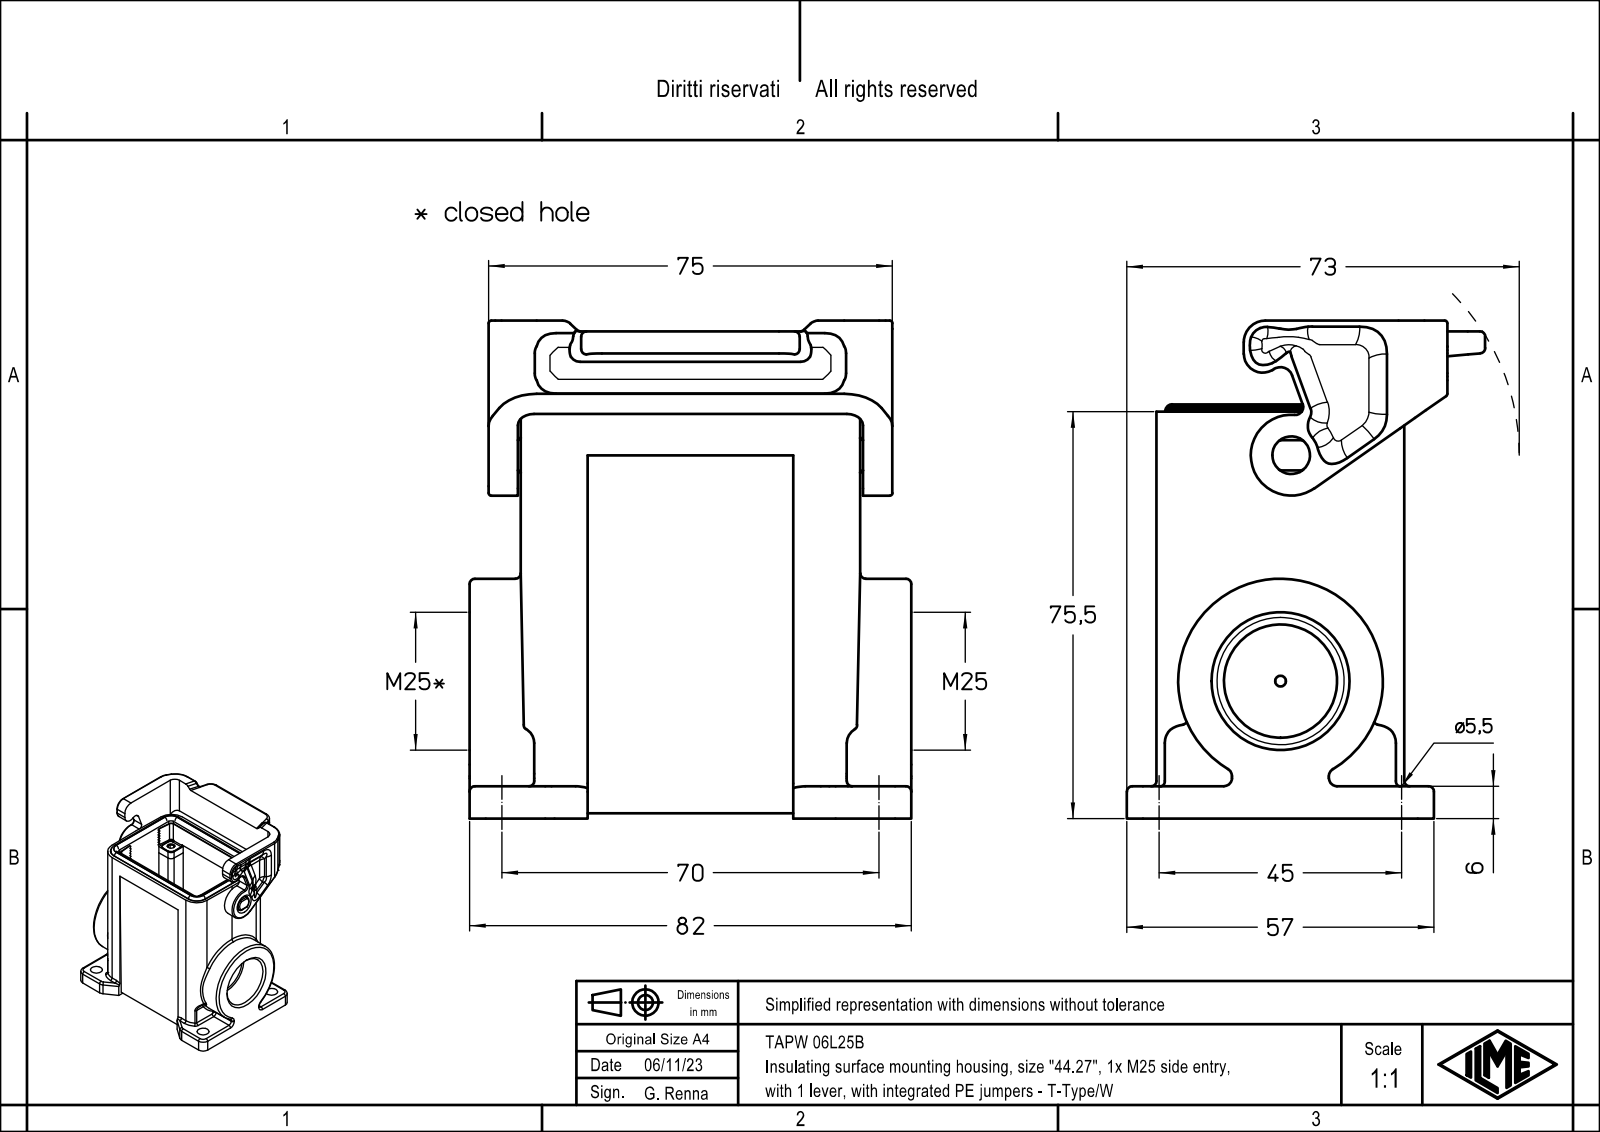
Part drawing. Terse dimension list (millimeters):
name: TAPW 06L25B
written by: Creo Elements/Direct Modeling 20.1B 02-Apr-2019 (C) Parametric Technology GmbH (AUTOMOTIVE_DESIGN)
unit: mm
bodies: 1 solid, 518 faces (318 planar, 164 cylindrical, 36 other)
size: 92.4 × 82 × 66.5
volume: 138 676 mm³; area: 50 113 mm²
holes: 4× ⌀3.5, 4× ⌀5.5, 1× ⌀21, 1× ⌀23.6
bosses: 1× ⌀38
rounds: 17× R1.5, 17× R3, 14× R2, 12× R1.3, 8× R1, 6× R0.5, 4× R1.6, 4× R6
face distances: 5.4, 40.6, 46, 35.2, 5.5, 14.9, 1, 9, 67.1, 58.1
hole spacings: 15.81, 38.28, 57.71, 67.42, 27, 44, 45, 51.62
